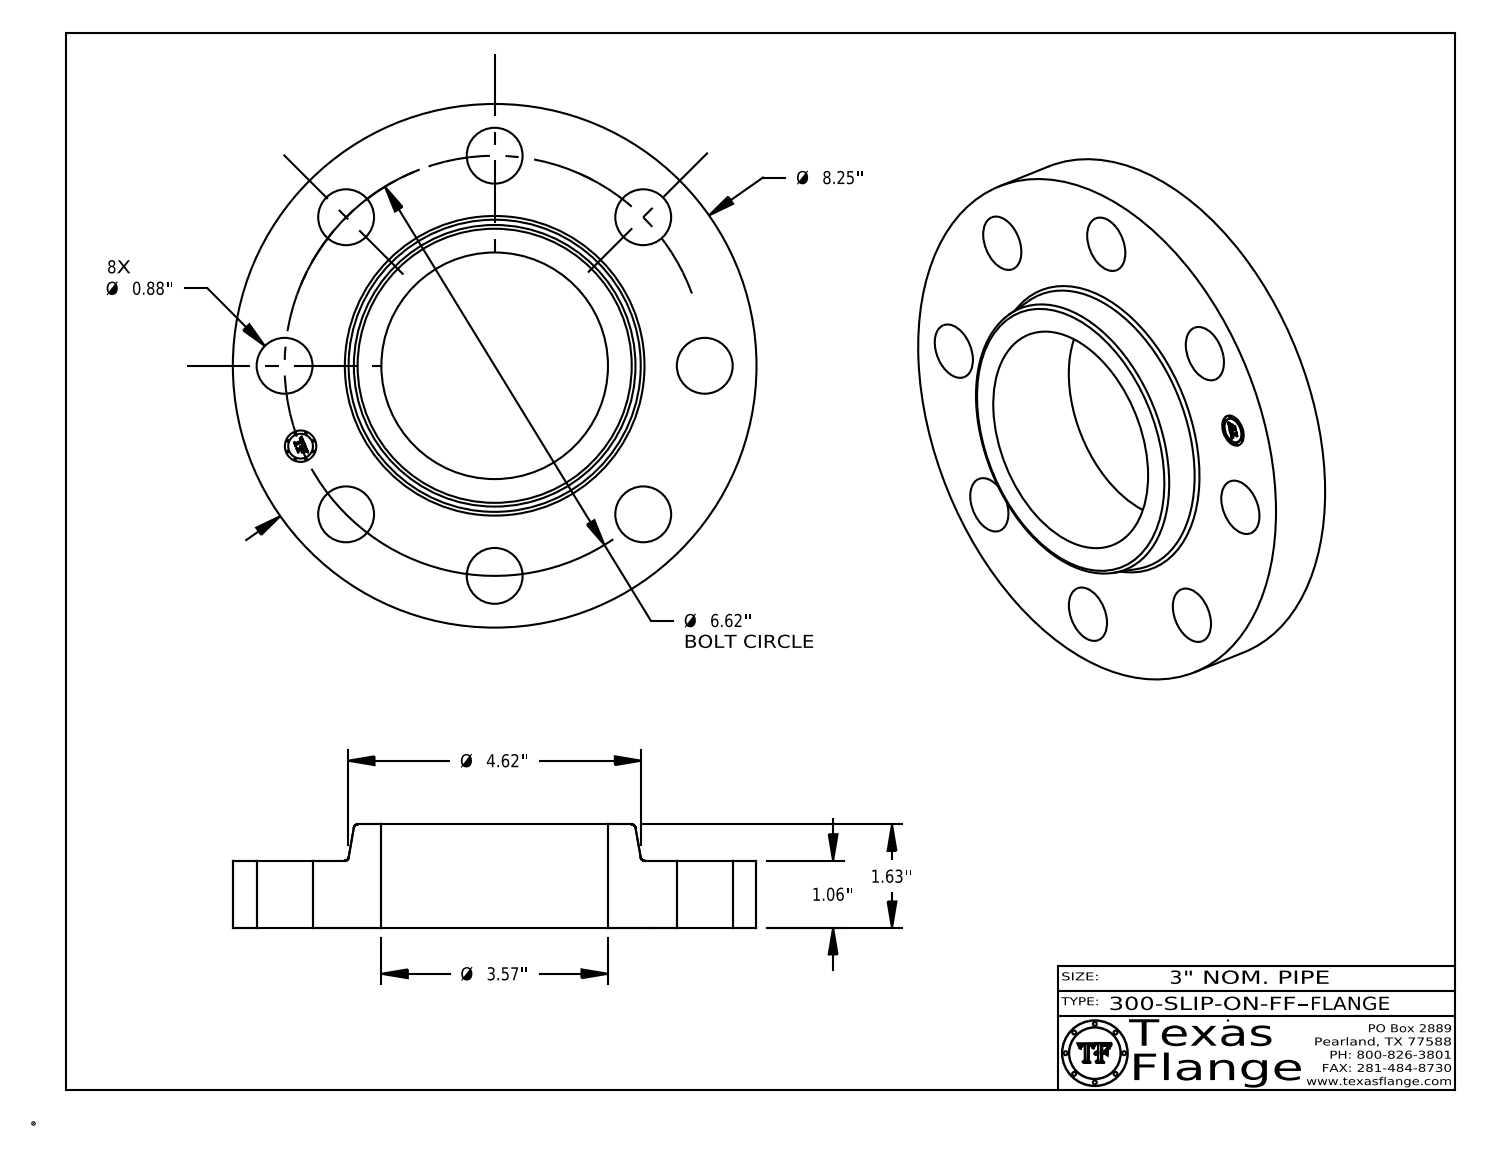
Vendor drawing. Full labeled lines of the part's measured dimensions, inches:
Part name (STEP PRODUCT): 300-SLIP-ON-FF
STEP written by: CATIA V5 STEP AP214 (AUTOMOTIVE_DESIGN)
Units: inches
Bodies: 1 solid, 415 faces (369 planar, 40 cylindrical, 6 other)
Overall size (bounding box): 8.25 × 8.25 × 1.63
Volume: 44.33 in³ · Surface area: 152.8 in²
Round holes (diameter × count): ⌀0.88 ×8, ⌀0.495 ×1, ⌀3.57 ×1
Round bosses / shafts (diameter × count): ⌀0.03 ×8, ⌀8.25 ×1, ⌀0.39 ×1
Main face-to-face distances: 1.06, 1.63, 0.57, 0.015, 1.045, 0.585, 0.148, 0.145, 0.027, 0.096
Hole centre spacings: 3.31, 2.533, 6.116, 4.681, 4.681, 1.291, 3.678, 6.493
